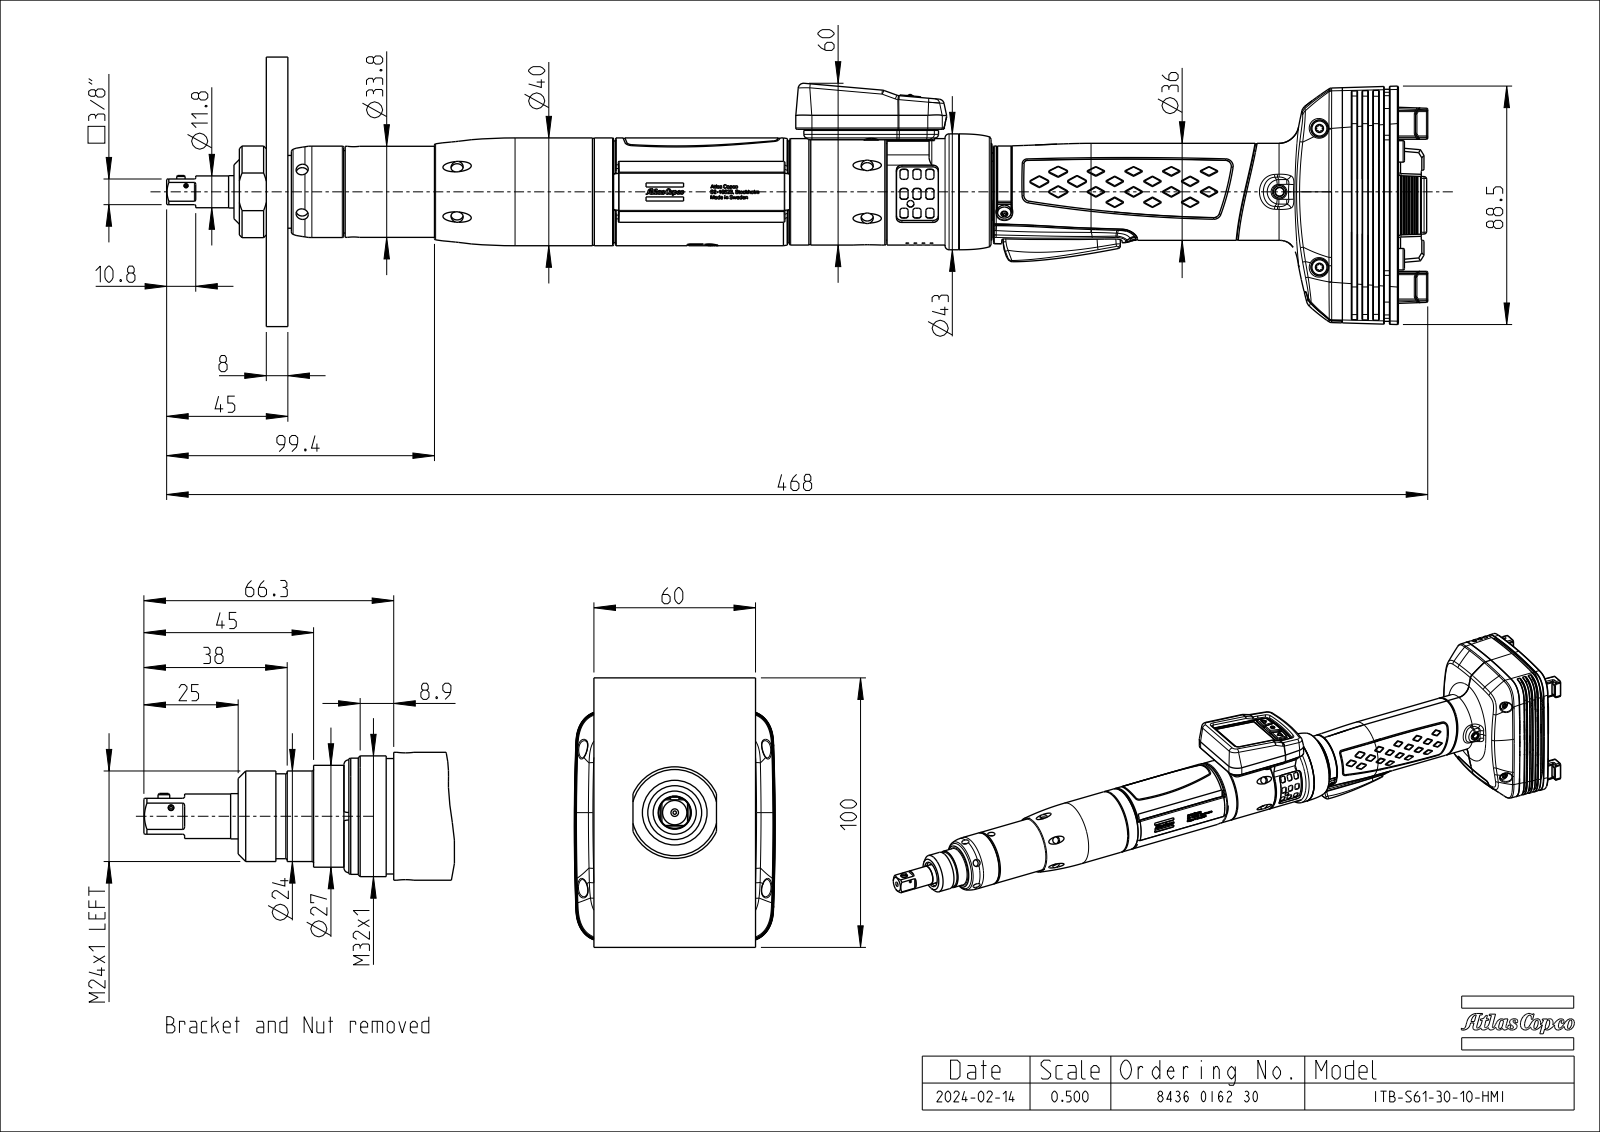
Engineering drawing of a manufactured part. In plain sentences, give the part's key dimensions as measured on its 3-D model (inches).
The part is named "EXT_COMP_SW0009". Its 3-D file was written by "CREO PARAMETRIC BY PTC INC, 2020281 (CONFIG_CONTROL_DESIGN)". It is 9 solids with 12518 faces: 4587 planar, 2832 cylindrical and 5099 other. Overall it measures 18.432 by 3.525 by 2.934 inches. Its volume is 29.94 cubic inches and its surface area 289.6 square inches. Round holes: 12 of diameter 0.039, 11 of diameter 0.177, 10 of diameter 0.126, 9 of diameter 0.098, 6 of diameter 0.118, 4 of diameter 0.087, 4 of diameter 0.13, 4 of diameter 0.169, 4 of diameter 0.228, 4 of diameter 0.256, 3 of diameter 0.157, 2 of diameter 0.063. Round bosses or shafts: 4 of diameter 0.244, 4 of diameter 0.217, 4 of diameter 0.157, 3 of diameter 0.22, 3 of diameter 0.197, 3 of diameter 0.138, 3 of diameter 0.118, 2 of diameter 0.098. Partial cylindrical surfaces (rounded edges, fillets, slot ends): 601 of radius 0.012, 248 of radius 0.02, 247 of radius 0.008, 127 of radius 0.039, 106 of radius 0.079, 42 of radius 0.004, 31 of radius 0.012, 30 of radius 0.059. The main face-to-face distances are 0.441, 0.199, 0.079, 0.118, 0.795, 0.354, 1.346, 0.909, 0.531, 0.016. The hole center spacings are 0.118, 0.236, 0.75, 2.184, 2.294, 3.077, 0.354, 2.266.
